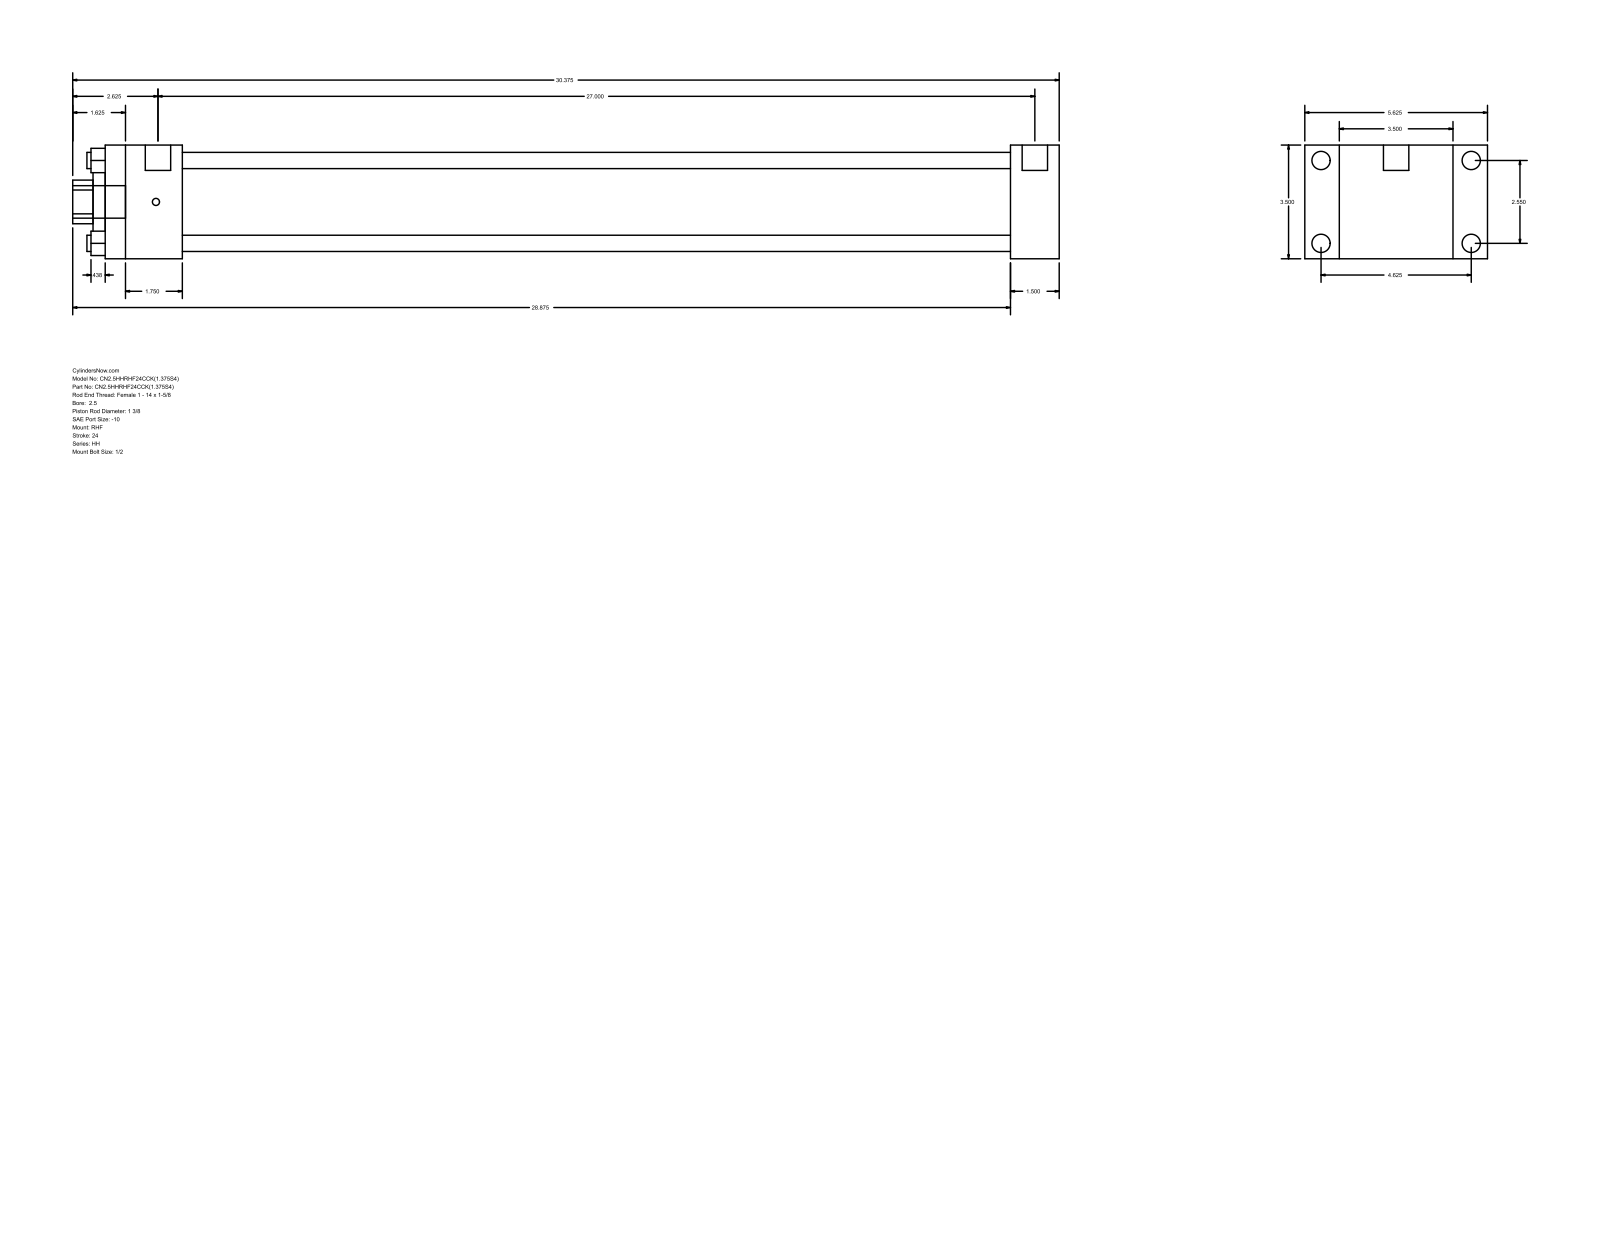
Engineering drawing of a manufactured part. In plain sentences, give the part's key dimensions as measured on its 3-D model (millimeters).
The part is named "HH_RHF__0250_1.375". Its 3-D file was written by "GSSL Pune (CONFIG_CONTROL_DESIGN)". It is 0 solids with 88 faces: 60 planar, 28 cylindrical and 0 other. Overall it measures 771.52 by 142.88 by 88.9 millimeters. Round holes: 4 of diameter 12.7, 1 of diameter 34.92, 1 of diameter 50.8, 1 of diameter 73.03. Round bosses or shafts: 4 of diameter 14.3, 4 of diameter 5.56, 2 of diameter 19.84, 1 of diameter 25.4. Partial cylindrical surfaces (rounded edges, fillets, slot ends): 1 of radius 17.06. The main face-to-face distances are 88.9, 38.1, 26.99, 115.89, 708.02, 746.12, 142.88, 60.32, 647.7, 685.8. The hole center spacings are 45.79, 64.76, 91.58.
